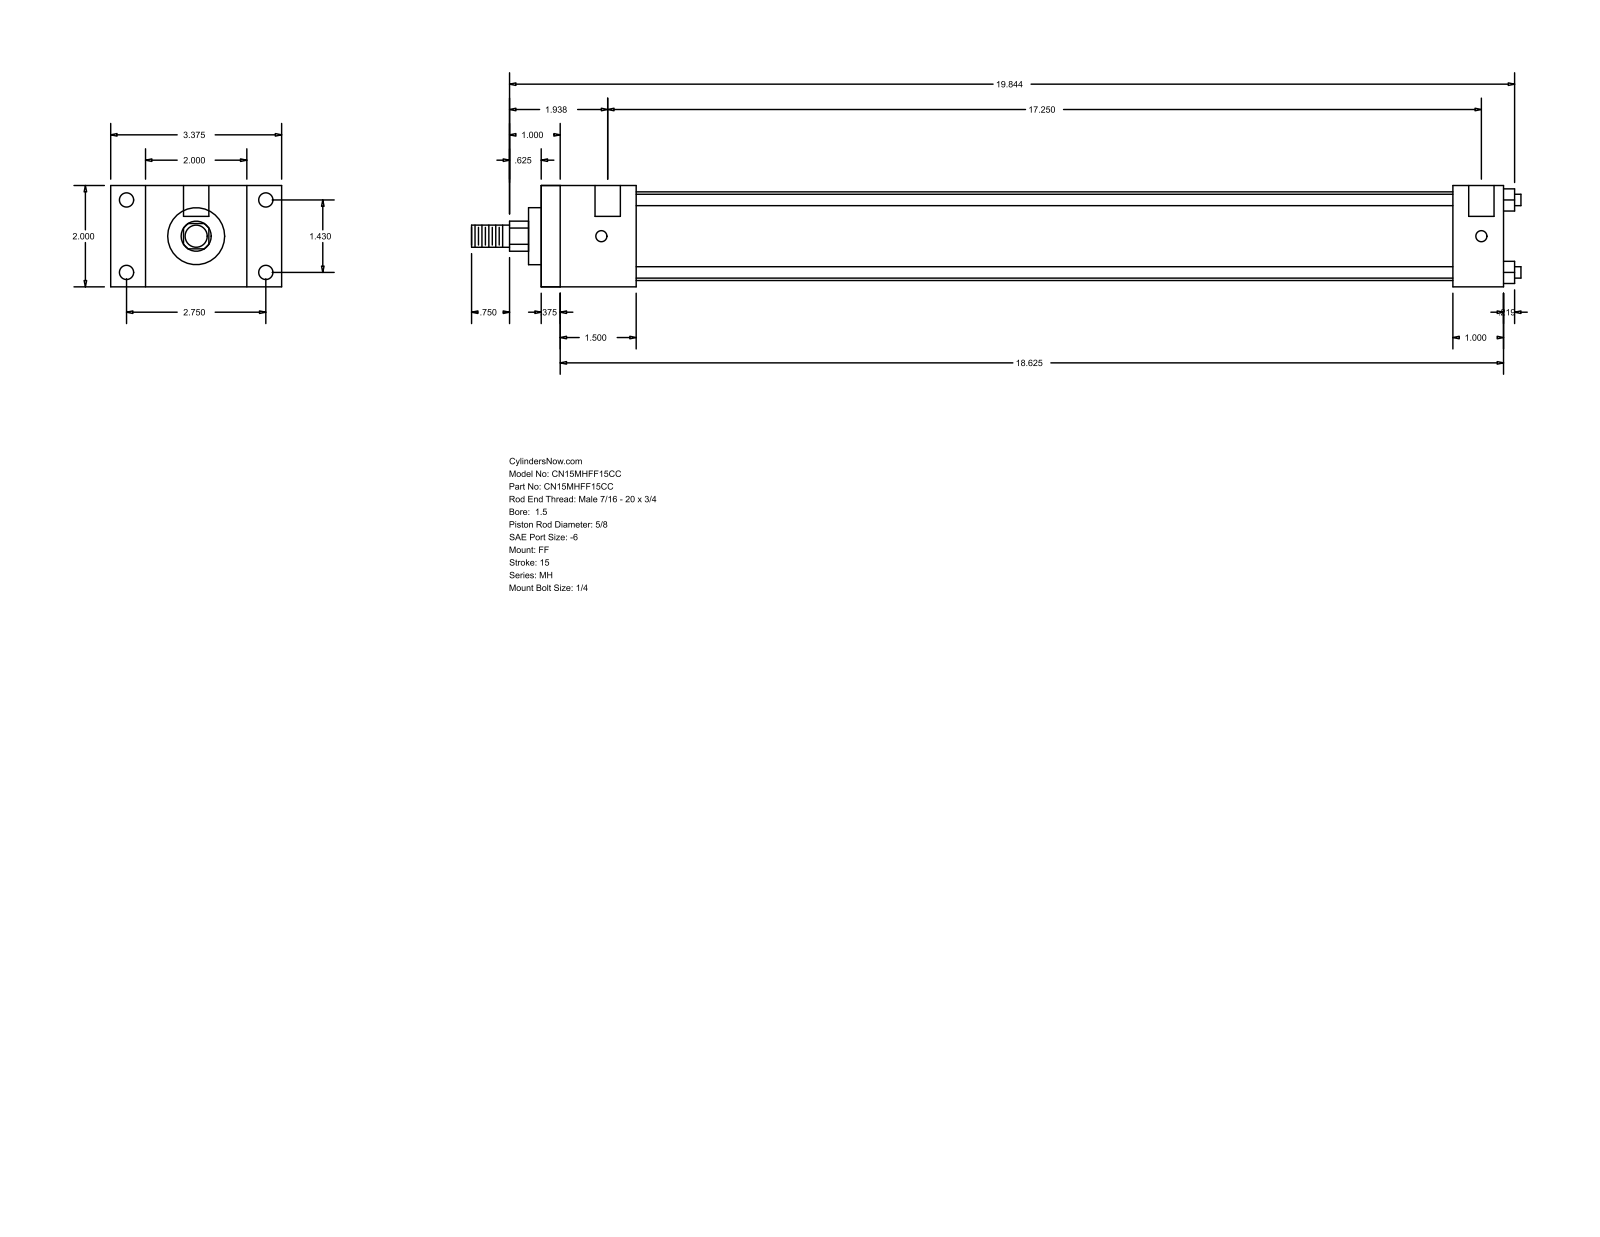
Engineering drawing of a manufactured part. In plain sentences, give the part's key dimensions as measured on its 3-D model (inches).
The part is named "MH_FF__0150_0.625". Its 3-D file was written by "GSSL Pune (CONFIG_CONTROL_DESIGN)". It is 0 solids with 92 faces: 64 planar, 28 cylindrical and 0 other. Overall it measures 20.719 by 3.375 by 2 inches. Round holes: 4 of diameter 0.219, 4 of diameter 0.281, 2 of diameter 0.5. Round bosses or shafts: 4 of diameter 0.225, 1 of diameter 1.75, 1 of diameter 1.125, 1 of diameter 0.625, 1 of diameter 0.437. Partial cylindrical surfaces (rounded edges, fillets, slot ends): 1 of radius 0.297. The main face-to-face distances are 2, 19, 0.375, 18.625, 0.687, 2.687, 1.875, 1.5, 17.125, 18. The hole center spacings are 1.43, 2.75, 3.099, 17.375, 0.125, 17.25.
